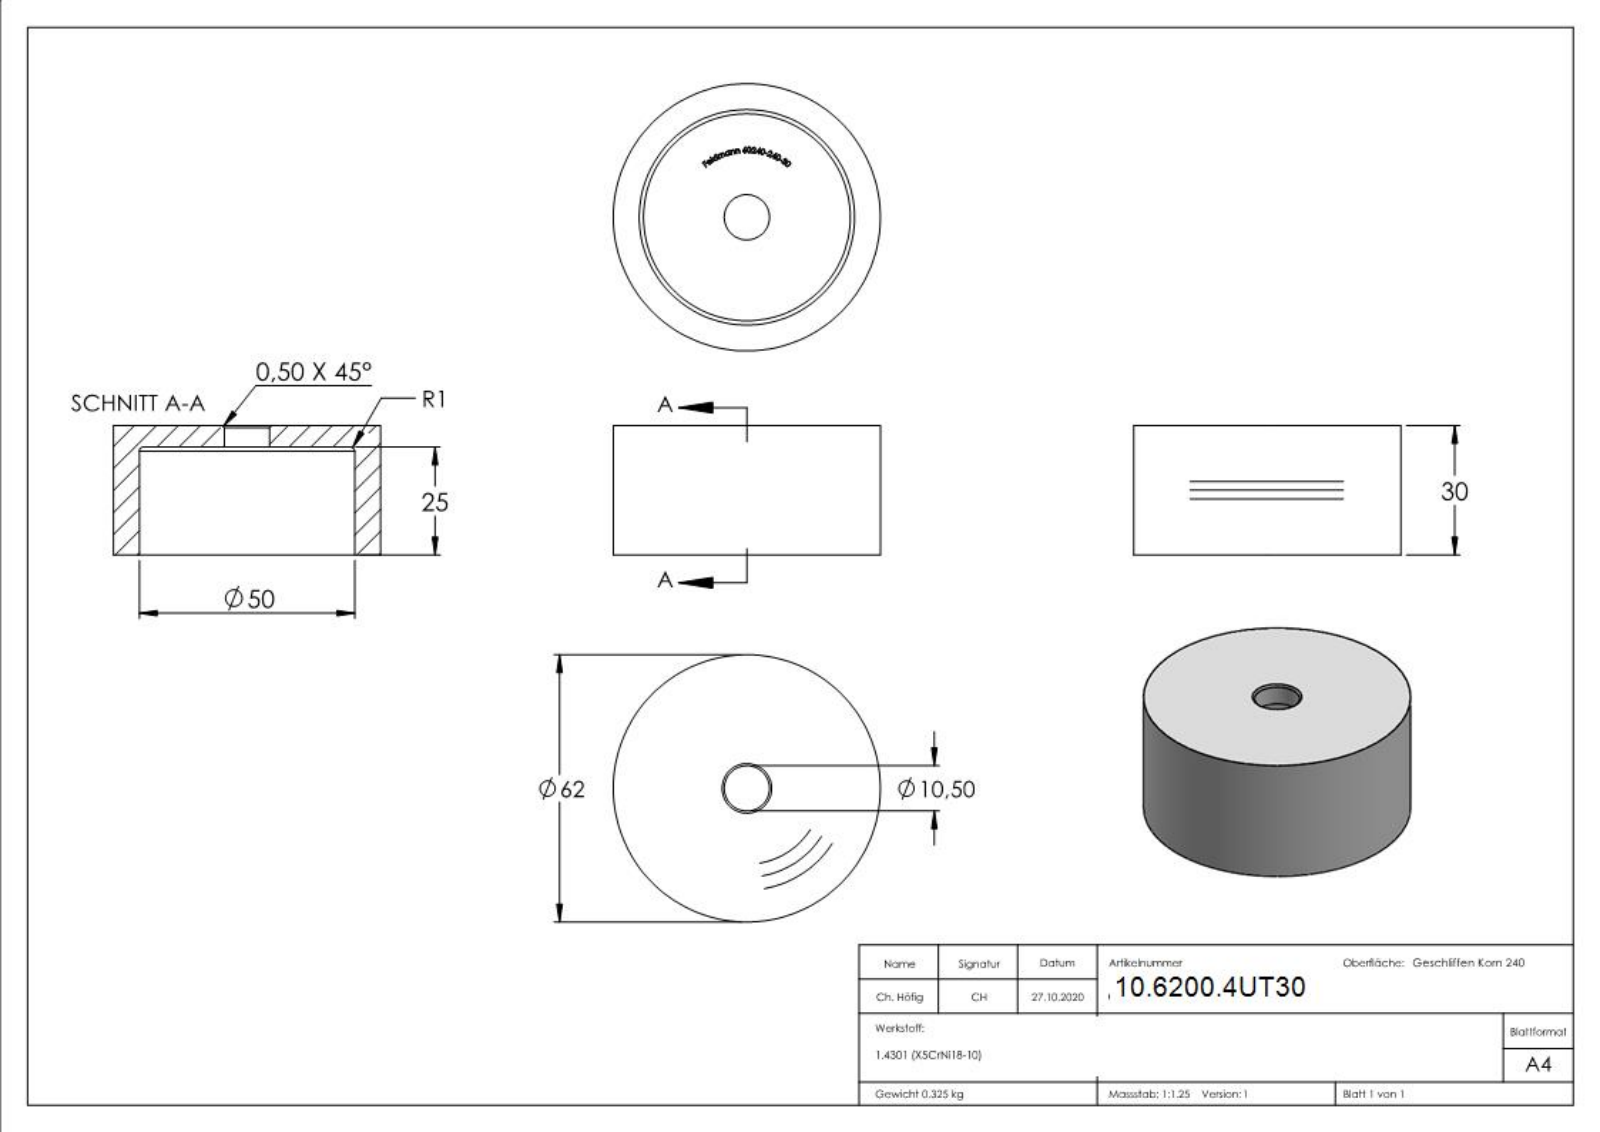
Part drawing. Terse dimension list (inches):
name: 60240-240-30
written by: SolidWorks 2018 (CONFIG_CONTROL_DESIGN)
unit: in
bodies: 1 solid, 268 faces (139 planar, 6 cylindrical, 123 other)
size: 2.441 × 2.441 × 1.181
volume: 2.507 in³; area: 24.39 in²
holes: 1× ⌀0.413, 1× ⌀1.969
bosses: 1× ⌀2.441
face distances: 0.197, 0.984, 1.181, 0.988, 0.193, 0.021, 0.052, 0.029, 0.057, 0.026
